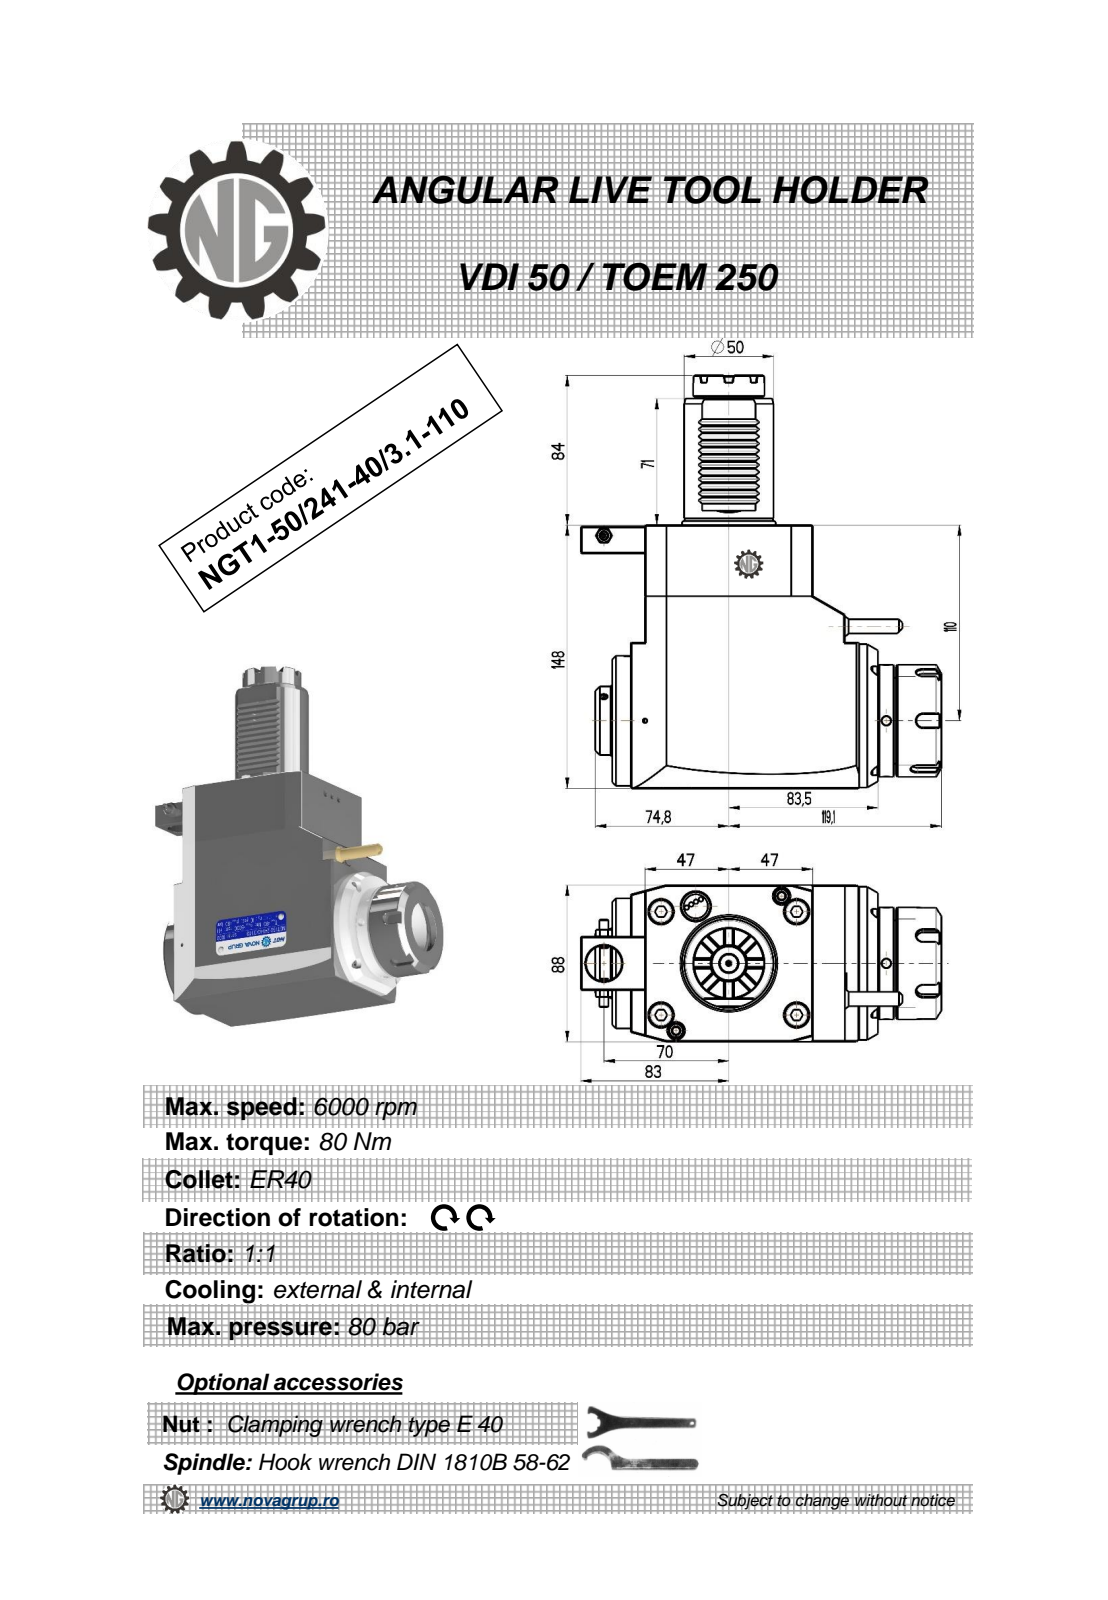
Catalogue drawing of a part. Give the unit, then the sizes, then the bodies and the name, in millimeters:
Units: millimetres
Overall size (bounding box): 232 × 202.1 × 88
Round holes (diameter × count): ⌀5 ×3, ⌀3 ×1, ⌀9.5 ×1, ⌀20 ×1, ⌀33.5 ×1
Round bosses / shafts (diameter × count): ⌀40 ×2, ⌀86 ×1, ⌀73 ×1, ⌀63 ×1, ⌀51 ×1, ⌀50 ×1, ⌀38.5 ×1, ⌀20.5 ×1
Partial cylindrical surfaces — rounded edges, fillets, slot ends (radius × count): R0.26 ×12, R0.3 ×12, R0.2 ×6, R3.75 ×5
Main face-to-face distances: 88, 148, 8, 94, 130.5, 36.5, 120, 18.3, 112.3, 148.8
Hole centre spacings: 52.46, 56.65, 101.5, 158.25
Volume: 1 854 000 mm³ · Surface area: 117 706 mm²
Bodies: 1 solid, 496 faces (245 planar, 94 cylindrical, 157 other)
Part name (STEP PRODUCT): NGT1_50_241_40_3_1_110
STEP written by: PRO/ENGINEER BY PARAMETRIC TECHNOLOGY CORPORATION, 2010280 (CONFIG_CONTROL_DESIGN)
